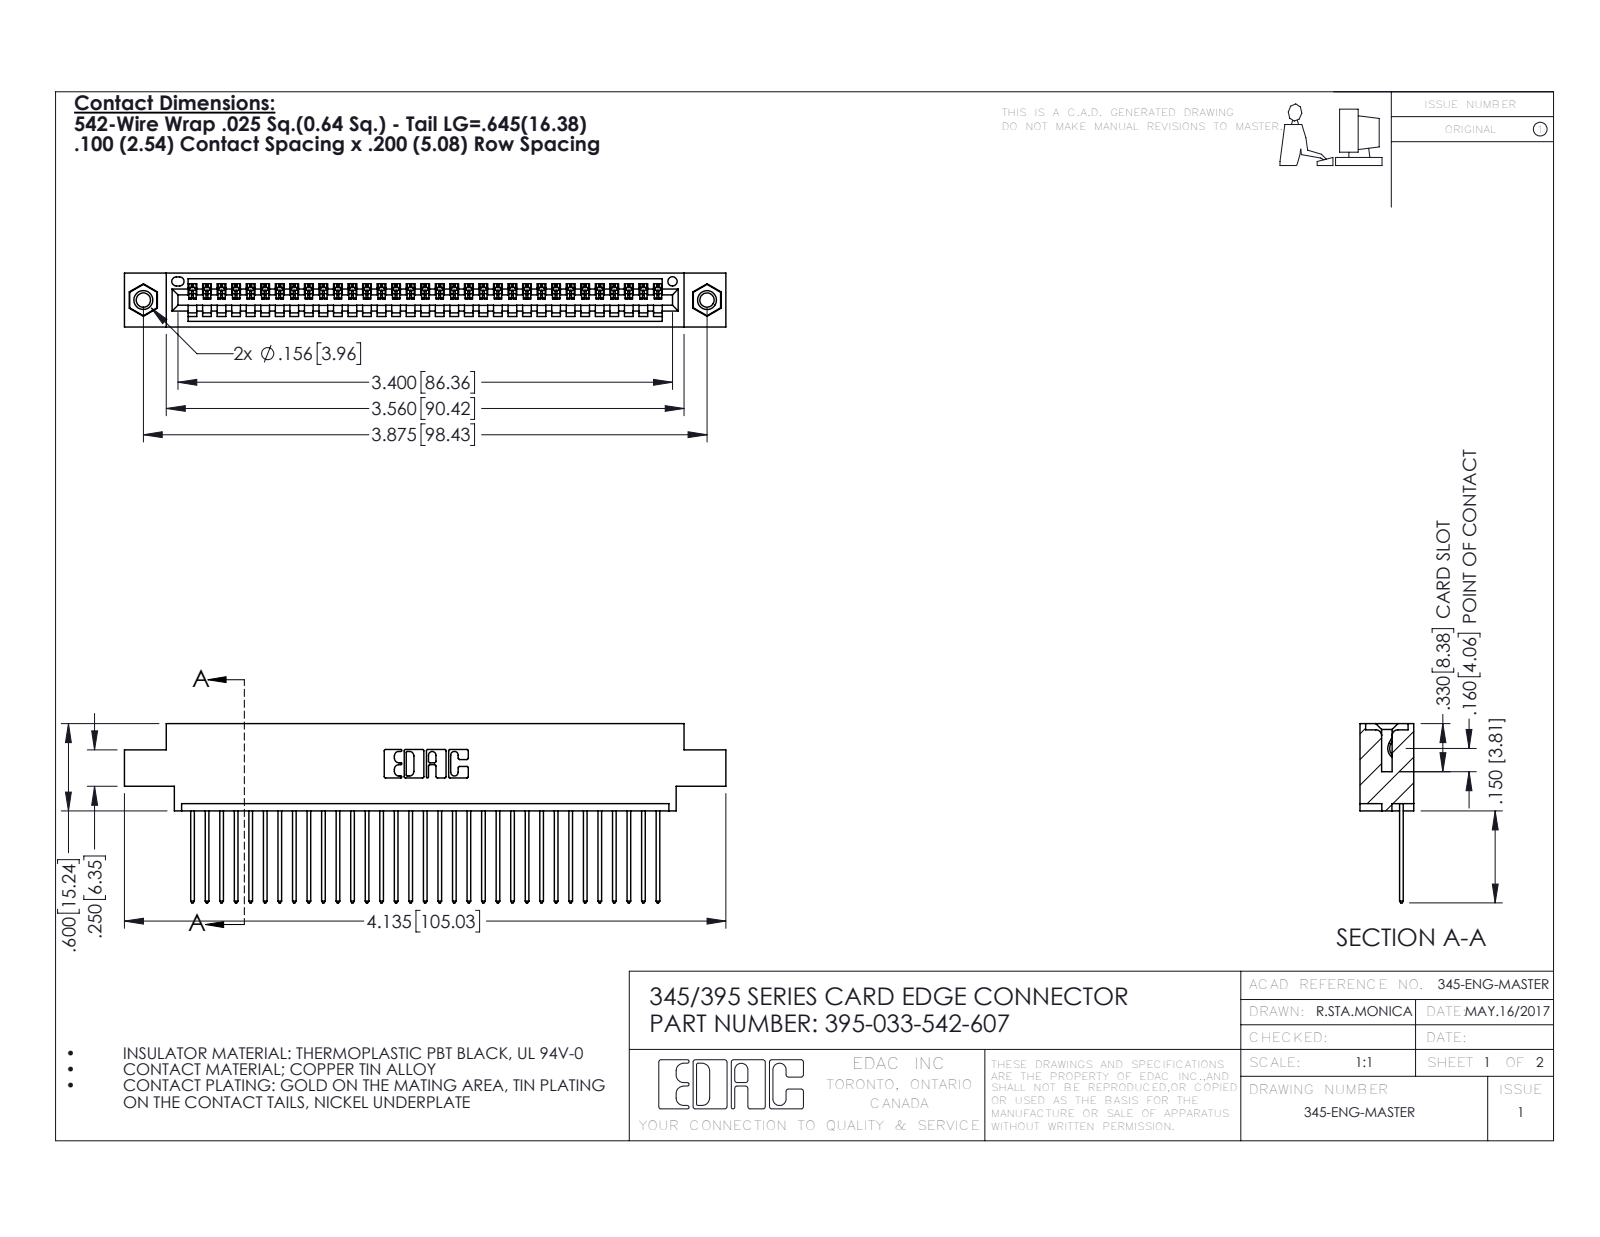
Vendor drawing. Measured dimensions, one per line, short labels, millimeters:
name: 395-033-542-607; 345 Part_0.170 Offset - 0.156 Dia-TI; 345-250-001_345-250-005-103; 345-292-001_345-293-142
written by: SolidWorks 2016 (CONFIG_CONTROL_DESIGN)
unit: mm
bodies: 36 solids, 2104 faces (1436 planar, 652 cylindrical, 16 other)
size: 105 × 31.3 × 9.4
volume: 9 850 mm³; area: 13 590 mm²
holes: 2× ⌀2.5, 2× ⌀3.2, 2× ⌀4, 1× ⌀1.6
bosses: 2× ⌀3.9
rounds: 66× R0.2, 66× R0.3, 22× R0.3, 6× R0.2, 6× R0.8, 3× R0.7, 2× R0.8, 2× R1
face distances: 1.8, 7.6, 9.4, 2.5, 6.9, 0.6, 5.1, 5.7, 4.4, 3.8
hole spacings: 6.9, 92.5, 98.4
